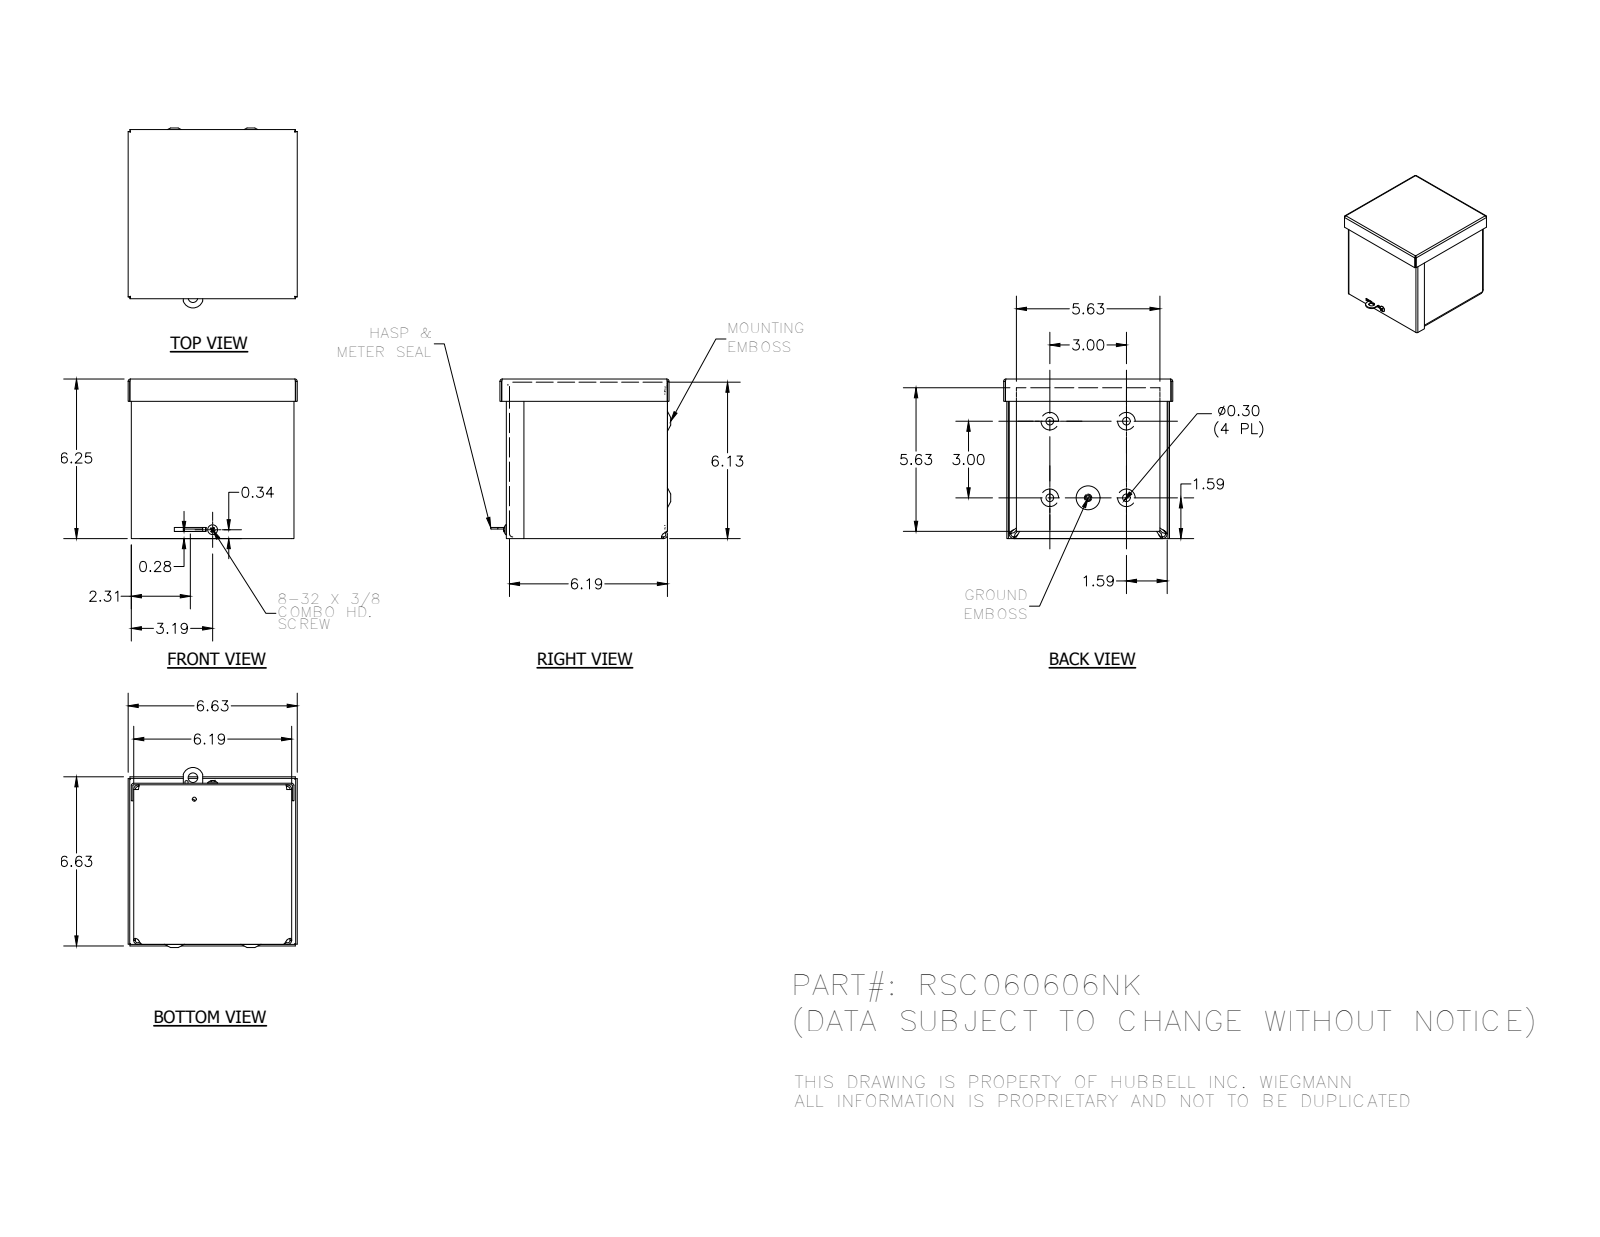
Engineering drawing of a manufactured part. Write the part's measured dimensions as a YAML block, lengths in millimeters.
part_name: "RSC060606NK_WRAP; RSC0606NK_LID; RSC0606NK_CAP; 3183 (+3 more)"
step_written_by: "Autodesk Inventor 2014 (AUTOMOTIVE_DESIGN)"
units: millimeters
bodies: {solids: 6, faces: 347, planar: 153, cylindrical: 73, other: 121}
overall_size: [180.97, 168.28, 158.76]
volume: 330009
surface_area: 426090
round_holes:
  - {diameter: 7.62, count: 4}
  - {diameter: 7.95, count: 2}
  - {diameter: 3.17, count: 1}
  - {diameter: 3.45, count: 1}
  - {diameter: 3.76, count: 1}
  - {diameter: 3.96, count: 1}
  - {diameter: 4.19, count: 1}
  - {diameter: 9.52, count: 1}
round_bosses_or_shafts:
  - {diameter: 9.75, count: 1}
  - {diameter: 5.8, count: 1}
  - {diameter: 4.17, count: 1}
partial_cylinders:
  - {radius: 0.79, count: 8}
  - {radius: 2.37, count: 8}
  - {radius: 3.17, count: 8}
  - {radius: 4.75, count: 8}
  - {radius: 1.4, count: 4}
  - {radius: 1.57, count: 4}
  - {radius: 2.38, count: 4}
  - {radius: 2.97, count: 4}
face_to_face_distances: [1.58, 155.59, 1.57, 157.17, 158.74, 3.15, 157.16, 158.73, 154.01, 157.15]
hole_center_spacings: [76.2, 38.1, 85.19, 107.76, 7.92, 19.73, 23.19, 31.79]
